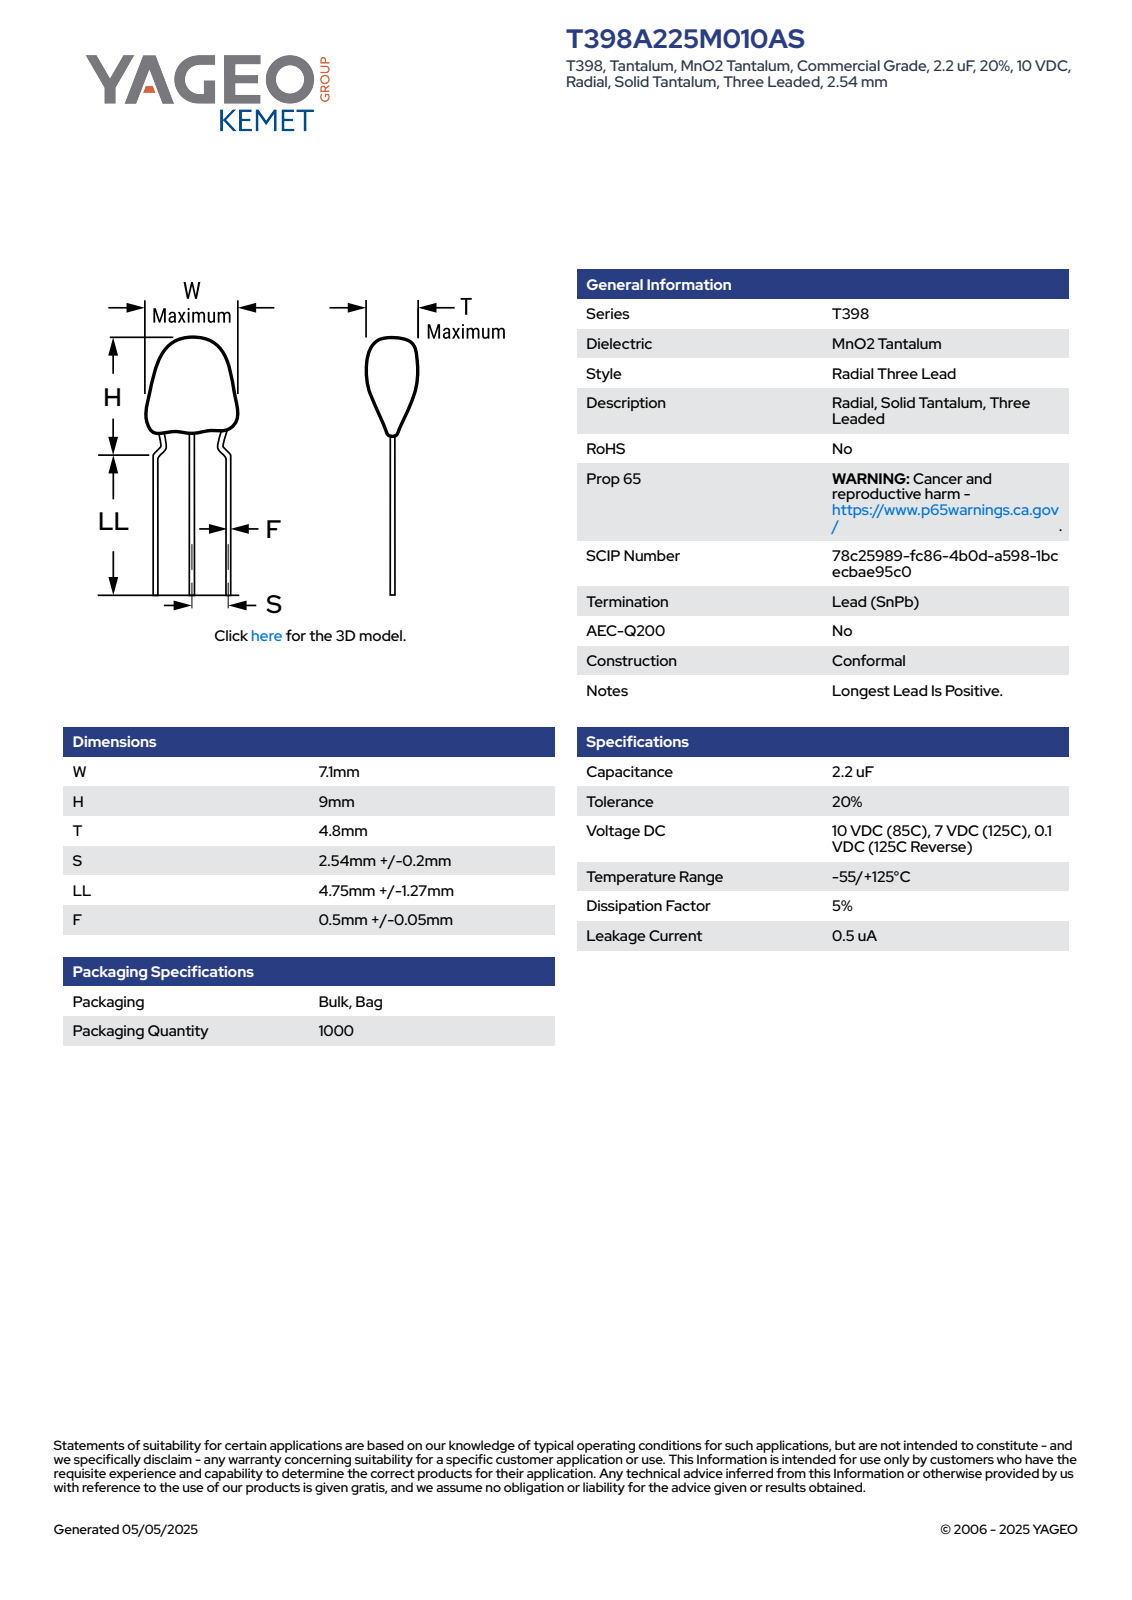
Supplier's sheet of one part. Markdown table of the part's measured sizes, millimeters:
| quantity | value |
| --- | --- |
| part name | CTR_T398_W7.1H9T4.8S2.54LL6.02F0.55 |
| STEP written by | SolidWorks 2014 (AUTOMOTIVE_DESIGN) |
| units | millimeters |
| bodies | 4 solids, 91 faces (67 planar, 8 cylindrical, 16 other) |
| overall size | 15.02 × 7.1 × 4.8 |
| volume | 235 mm³ |
| surface area | 246 mm² |
| round bosses / shafts (diameter × count) | 0.55 × 3 |
| partial cylindrical surfaces (radius × count) | 5 × 2 |
| main face-to-face distances | 4.8, 7.1, 7.12, 11.95, 4.83, 11.04, 3.92, 0.91, 0.92, 0.34 |
